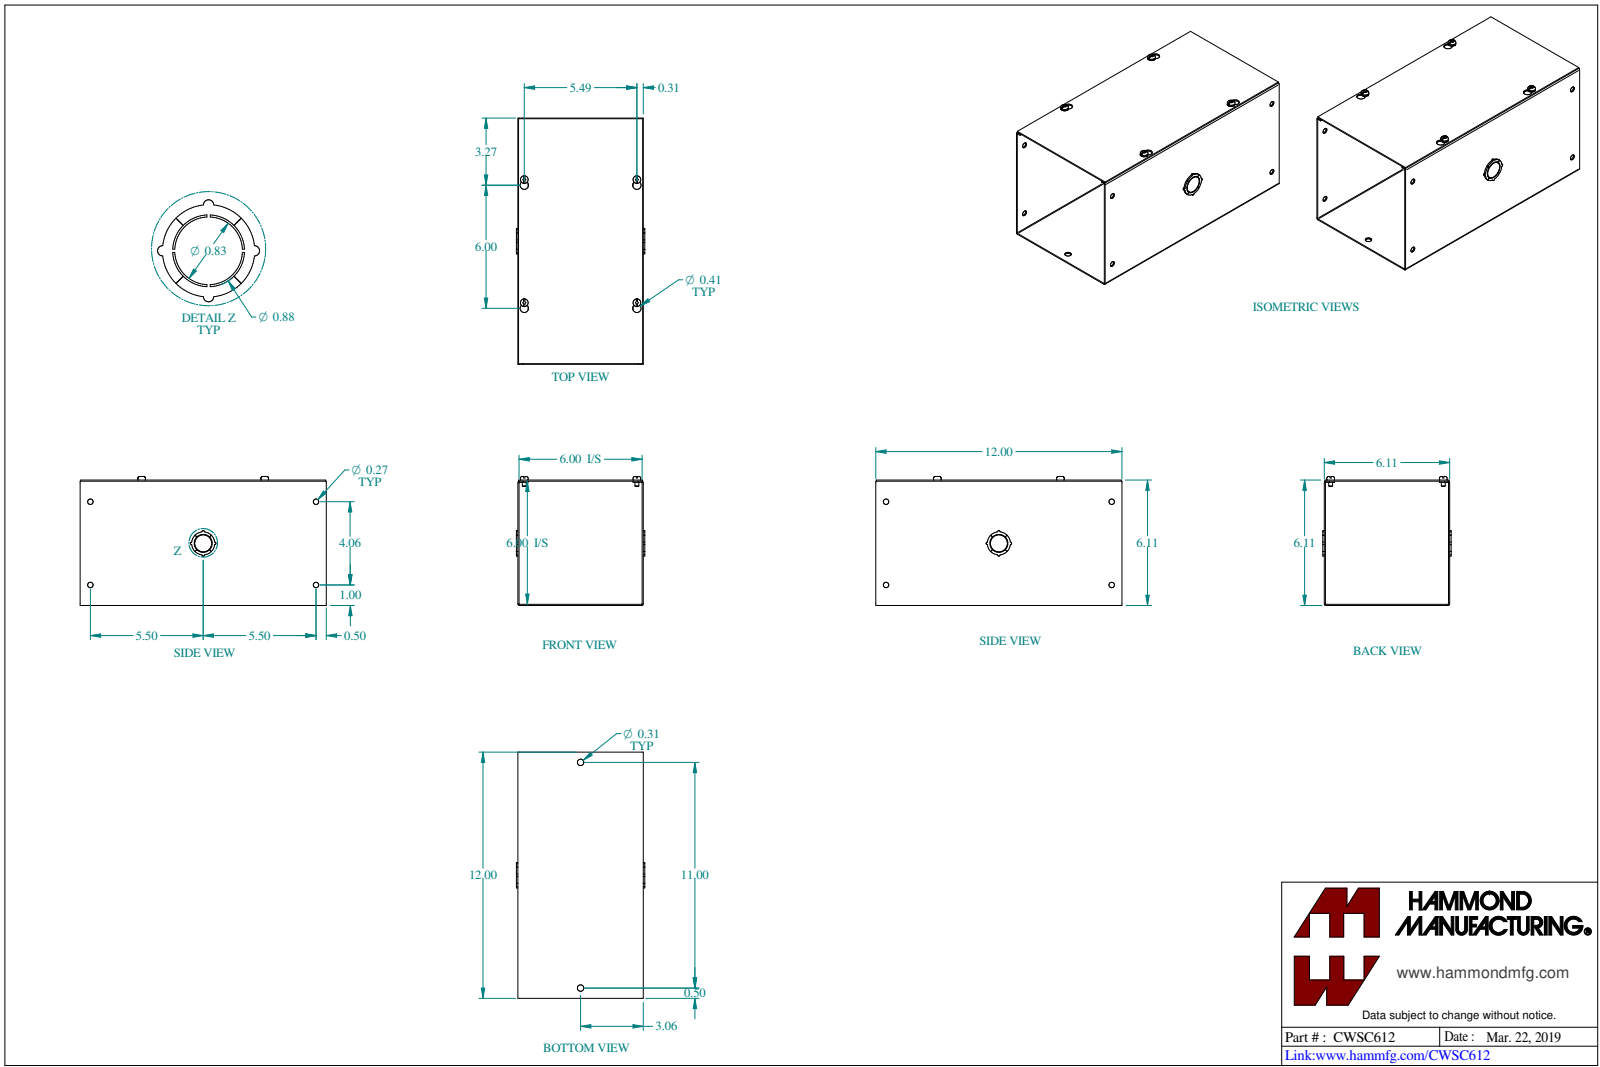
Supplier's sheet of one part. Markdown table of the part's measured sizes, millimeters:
| quantity | value |
| --- | --- |
| part name | CWSC612 |
| STEP written by | SolidWorks 2023 (CONFIG_CONTROL_DESIGN) |
| units | millimeters |
| bodies | 6 solids, 264 faces (122 planar, 118 cylindrical, 24 other) |
| overall size | 304.8 × 159.7 × 159 |
| volume | 280 900 mm³ |
| surface area | 389 400 mm² |
| round holes (diameter × count) | 4.5 × 4, 6.8 × 4, 8 × 2, 22.2 × 1 |
| round bosses / shafts (diameter × count) | 9.5 × 4, 4.8 × 4, 28.6 × 1, 21 × 1 |
| partial cylindrical surfaces (radius × count) | 0.7 × 4, 1.6 × 4, 2.2 × 4, 3.2 × 4, 5.2 × 4, 1.6 × 1 |
| main face-to-face distances | 1.4, 153.8, 152.4, 155.3, 151, 2.9, 0.8, 1.8, 3.3, 155.7 |
| hole center spacings | 94.3, 148.9, 226.9, 279.4, 103, 139.4, 152.4, 206.6 |
